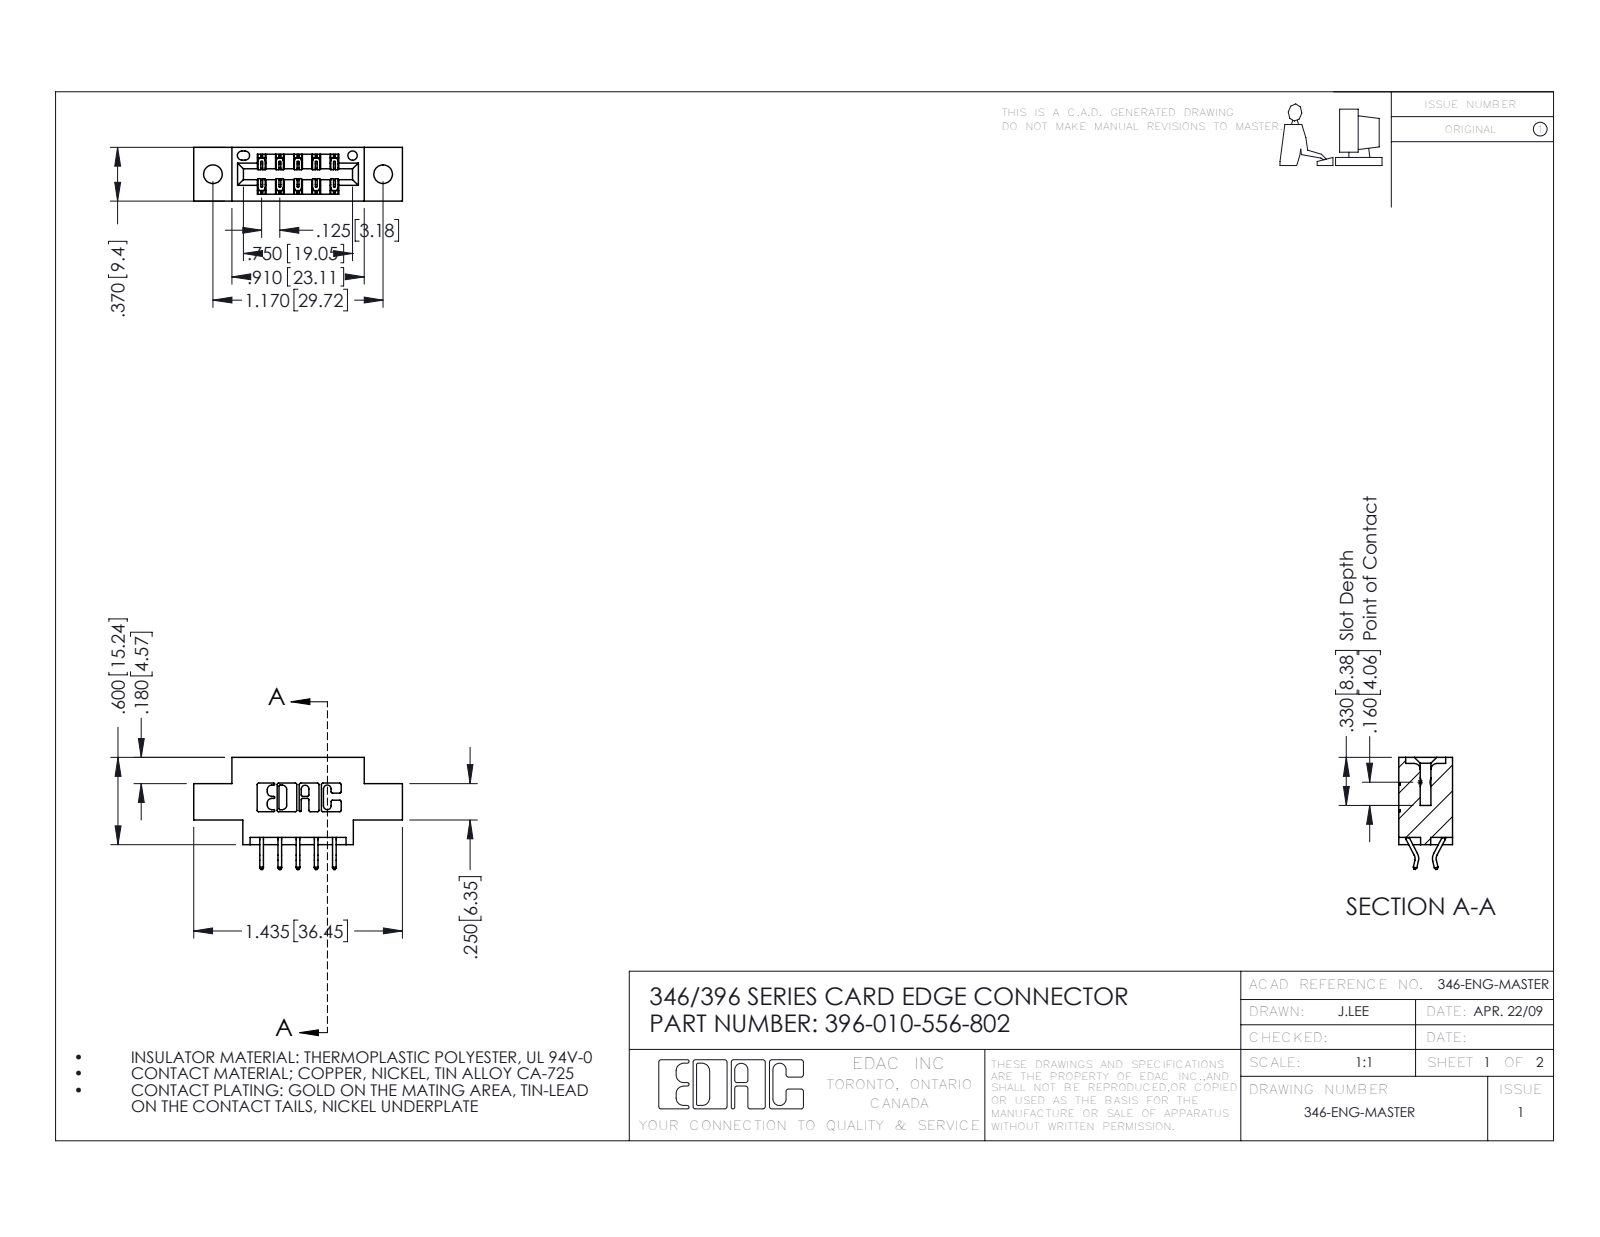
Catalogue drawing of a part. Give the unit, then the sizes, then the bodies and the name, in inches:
Units: inches
Overall size (bounding box): 1.435 × 0.77 × 0.37
Round holes (diameter × count): ⌀0.128 ×2, ⌀0.064 ×1
Partial cylindrical surfaces — rounded edges, fillets, slot ends (radius × count): R0.01 ×22, R0.006 ×15, R0.007 ×6, R0.031 ×6, R0.026 ×3, R0.01 ×2, R0.014 ×2, R0.022 ×2
Main face-to-face distances: 0.25, 0.37, 0.048, 0.322, 0.148, 0.222, 0.1, 0.174, 0.025, 0.072
Hole centre spacings: 0.246, 0.969, 1.17
Volume: 0.188 in³ · Surface area: 5.497 in²
Bodies: 11 solids, 706 faces (470 planar, 236 cylindrical, 0 other)
Part name (STEP PRODUCT): 345-292-001_556 Tail; 346 Part_0.170 Offset - 0.128 Dia; 396-010-556-802
STEP written by: SolidWorks 2016 (CONFIG_CONTROL_DESIGN)
